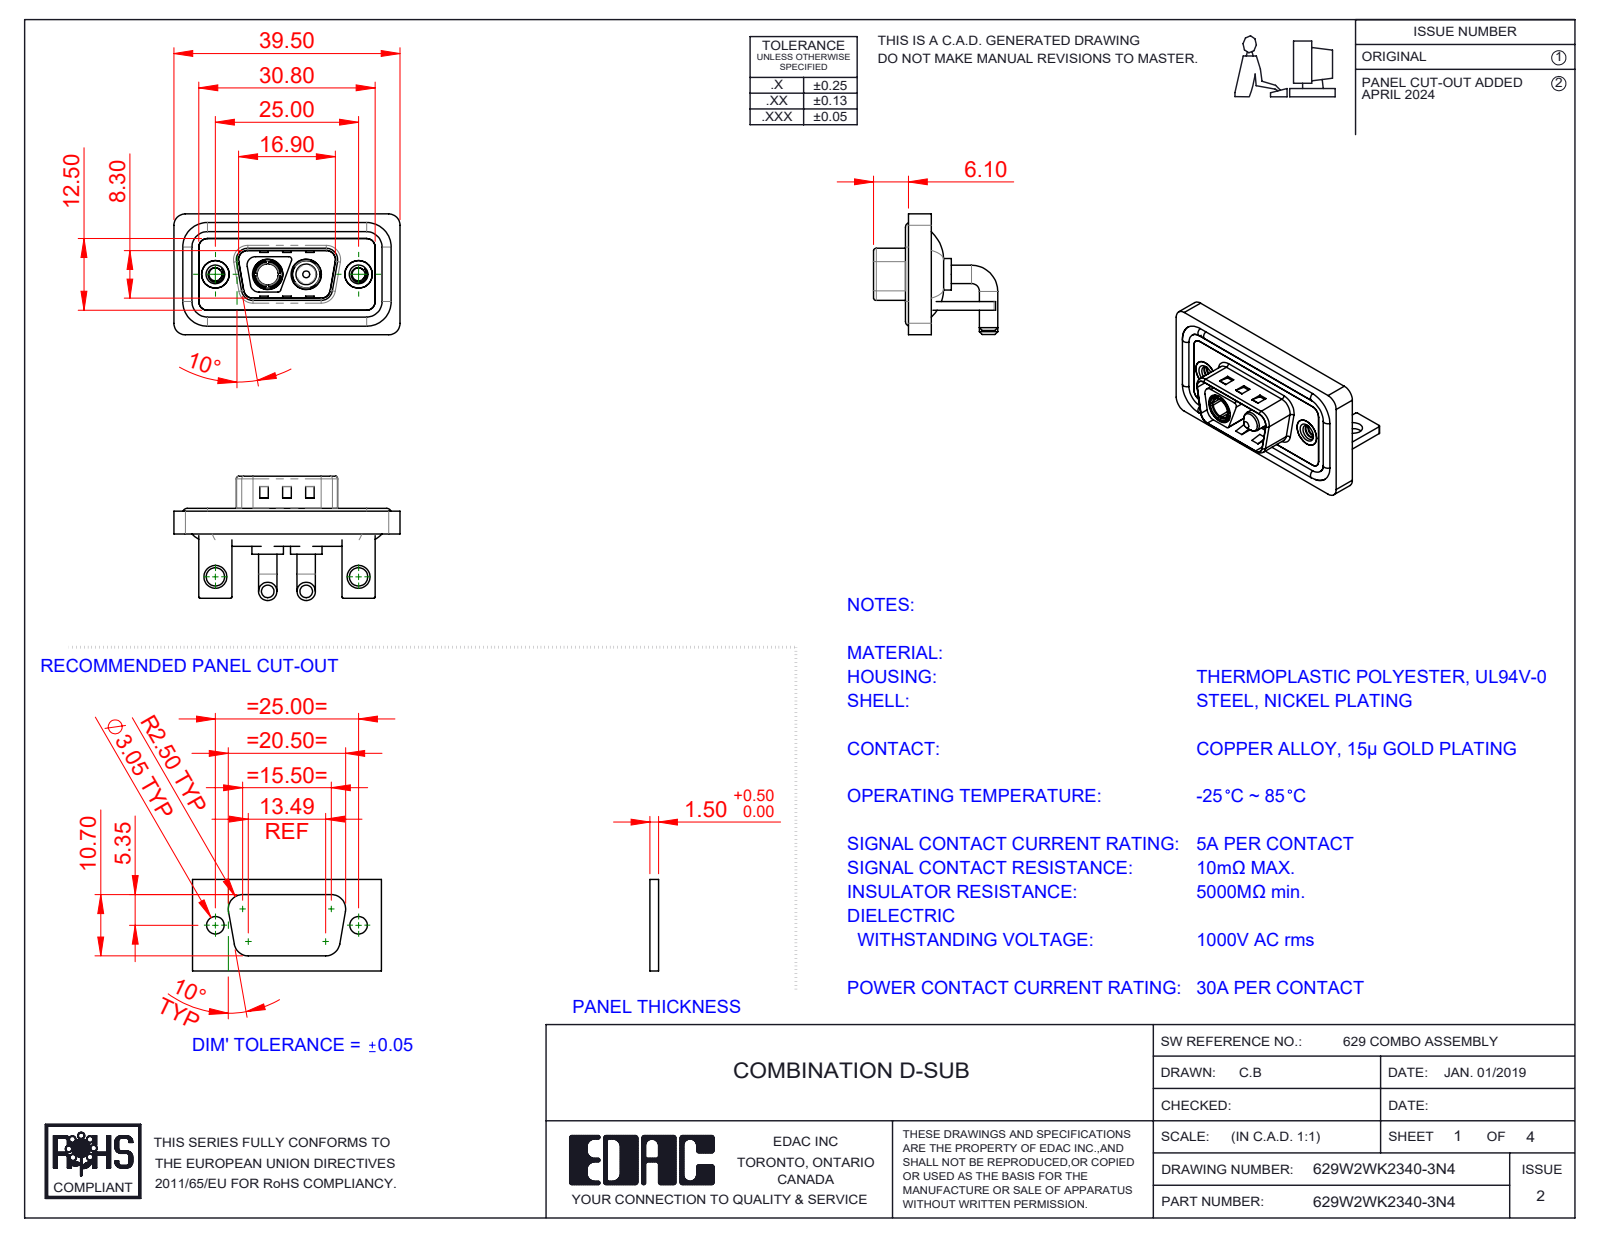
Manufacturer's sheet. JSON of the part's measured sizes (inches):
{"part_name": "629Combo Waterproof Housing_09 Contacts; 629Combo Housing_2WK2; Power Pin_30A RA; 629Combo Stabilizer Bracket (+5 more)", "step_written_by": "SolidWorks 2023 (CONFIG_CONTROL_DESIGN)", "units": "inches", "bodies": {"solids": 13, "faces": 582, "planar": 209, "cylindrical": 249, "other": 124}, "overall_size": [1.555, 0.854, 0.831], "volume_in3": 0.306, "surface_area_in2": 12.64, "round_holes": [[0.089, 2], [0.126, 2], [0.157, 2], [0.189, 2], [0.191, 2], [0.197, 2], [0.209, 2], [0.146, 1]], "round_bosses_or_shafts": [[0.126, 4], [0.063, 4], [0.217, 2], [0.205, 2], [0.193, 2], [0.187, 2], [0.148, 2], [0.195, 1]], "partial_cylinders_radius": [[0.059, 20], [0.079, 19], [0.01, 16], [0.02, 11], [0.063, 8], [0.024, 4], [0.026, 4], [0.035, 4]], "face_to_face_distances": [0.016, 0.059, 0.114, 0.031, 0.043, 0.047, 0.083, 0.063, 0.146, 0.098], "hole_center_spacings": [0.36, 0.624, 0.984, 0.265]}
